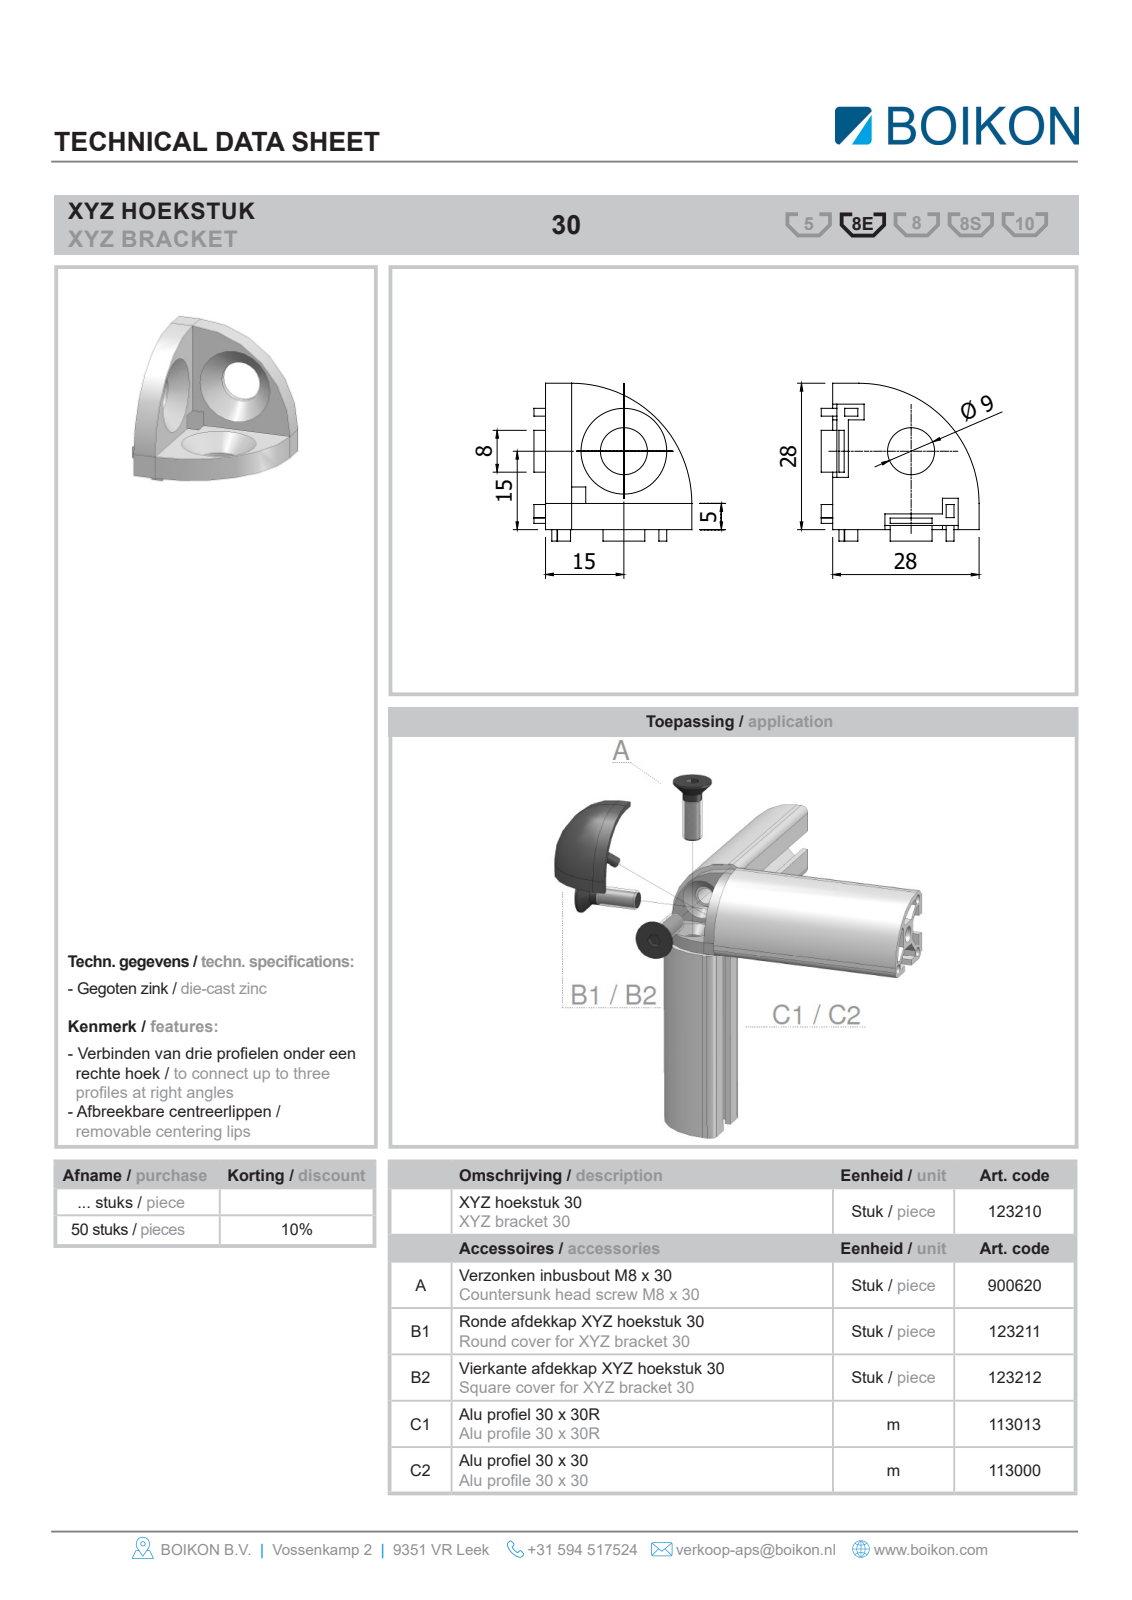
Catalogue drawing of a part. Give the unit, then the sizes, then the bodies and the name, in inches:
Units: inches
Overall size (bounding box): 2.049 × 2.049 × 2.049
Round holes (diameter × count): ⌀0.354 ×3
Round bosses / shafts (diameter × count): ⌀0.63 ×3, ⌀0.315 ×3, ⌀0.255 ×3
Partial cylindrical surfaces — rounded edges, fillets, slot ends (radius × count): R0.906 ×3
Main face-to-face distances: 0.197, 0.038, 0.235, 0.087, 0.031, 0.203, 0.165, 0.118, 0.059, 0.106
Volume: 0.645 in³ · Surface area: 11.89 in²
Bodies: 4 solids, 161 faces (131 planar, 18 cylindrical, 12 other)
Part name (STEP PRODUCT): Root; 123210XYZ HOEKSTUK 30BOIKON; 900620Verz. inbusbout DIN 7991 EV M8 x 30BOIKON0
STEP written by: HiCAD 2013 1802.4 Build 509 (AUTOMOTIVE_DESIGN)
